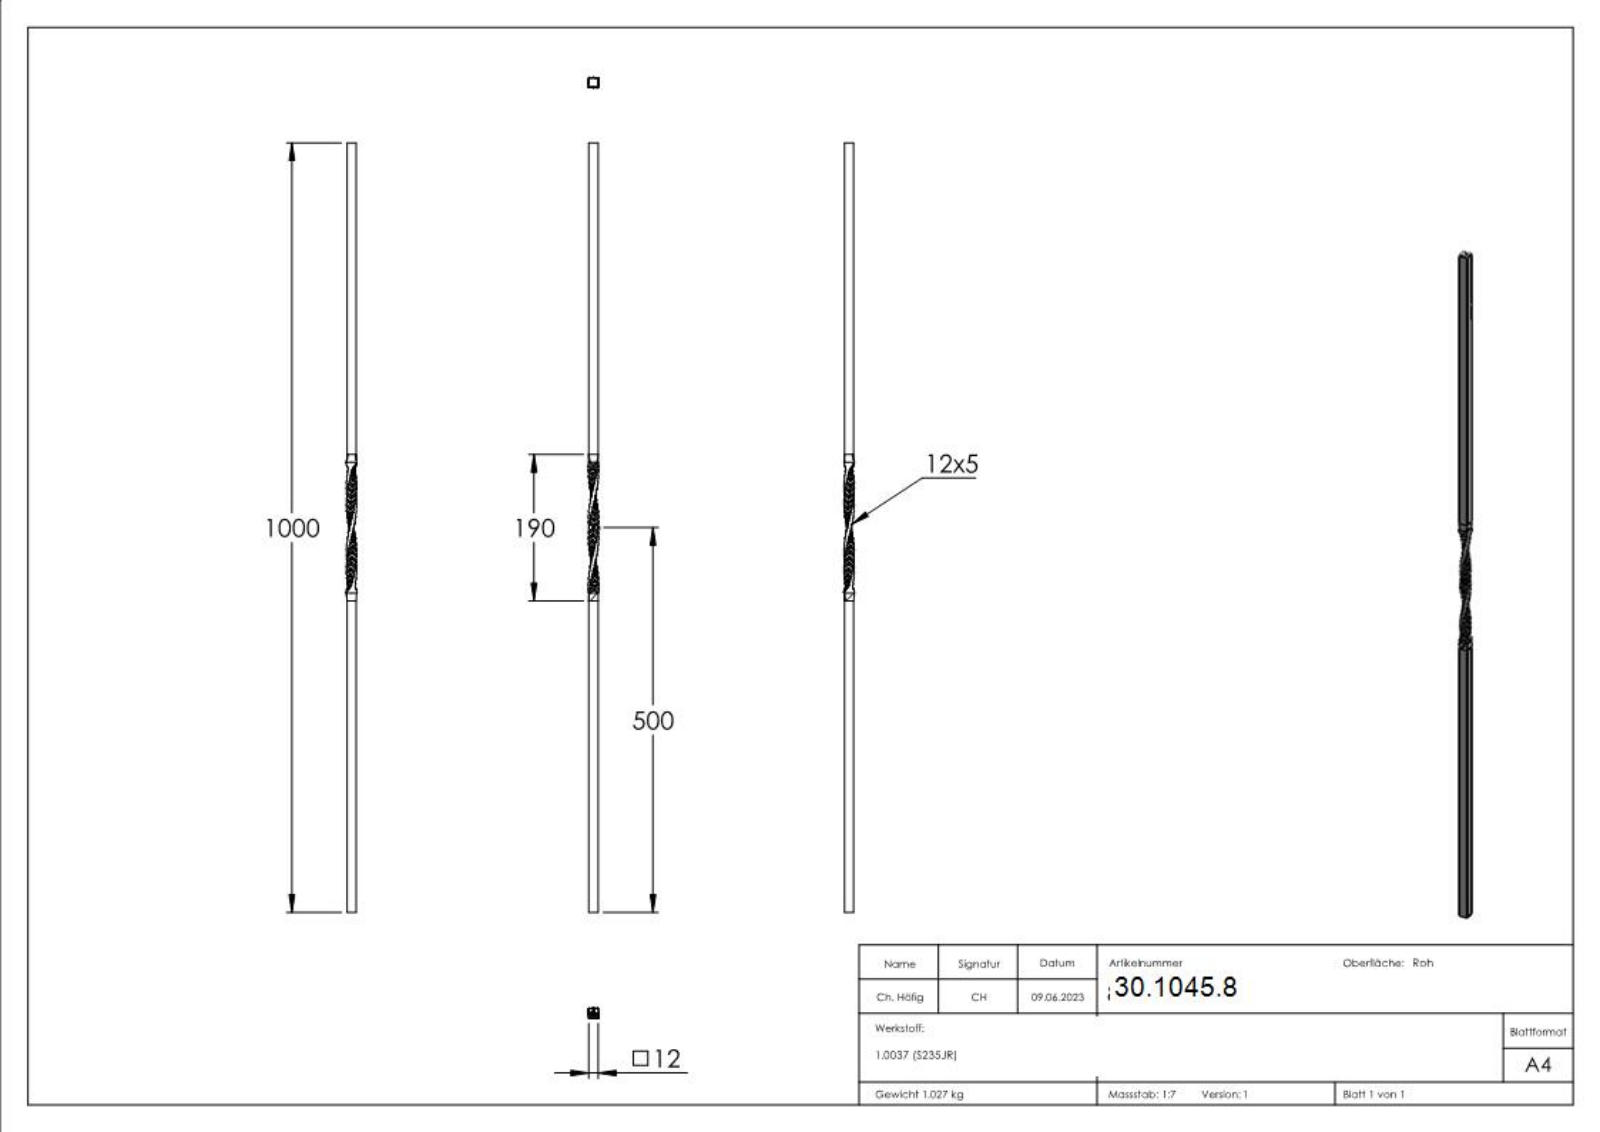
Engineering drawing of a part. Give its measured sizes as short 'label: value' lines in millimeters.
name: 8029-15
written by: SolidWorks 2018 (CONFIG_CONTROL_DESIGN)
unit: mm
bodies: 1 solid, 701 faces (152 planar, 0 cylindrical, 549 other)
size: 1000 × 18.18 × 14.17
volume: 131 700 mm³; area: 46 704 mm²
face distances: 12, 1000, 999.9, 415, 585, 414.9, 1.76, 5.04, 170, 584.9
